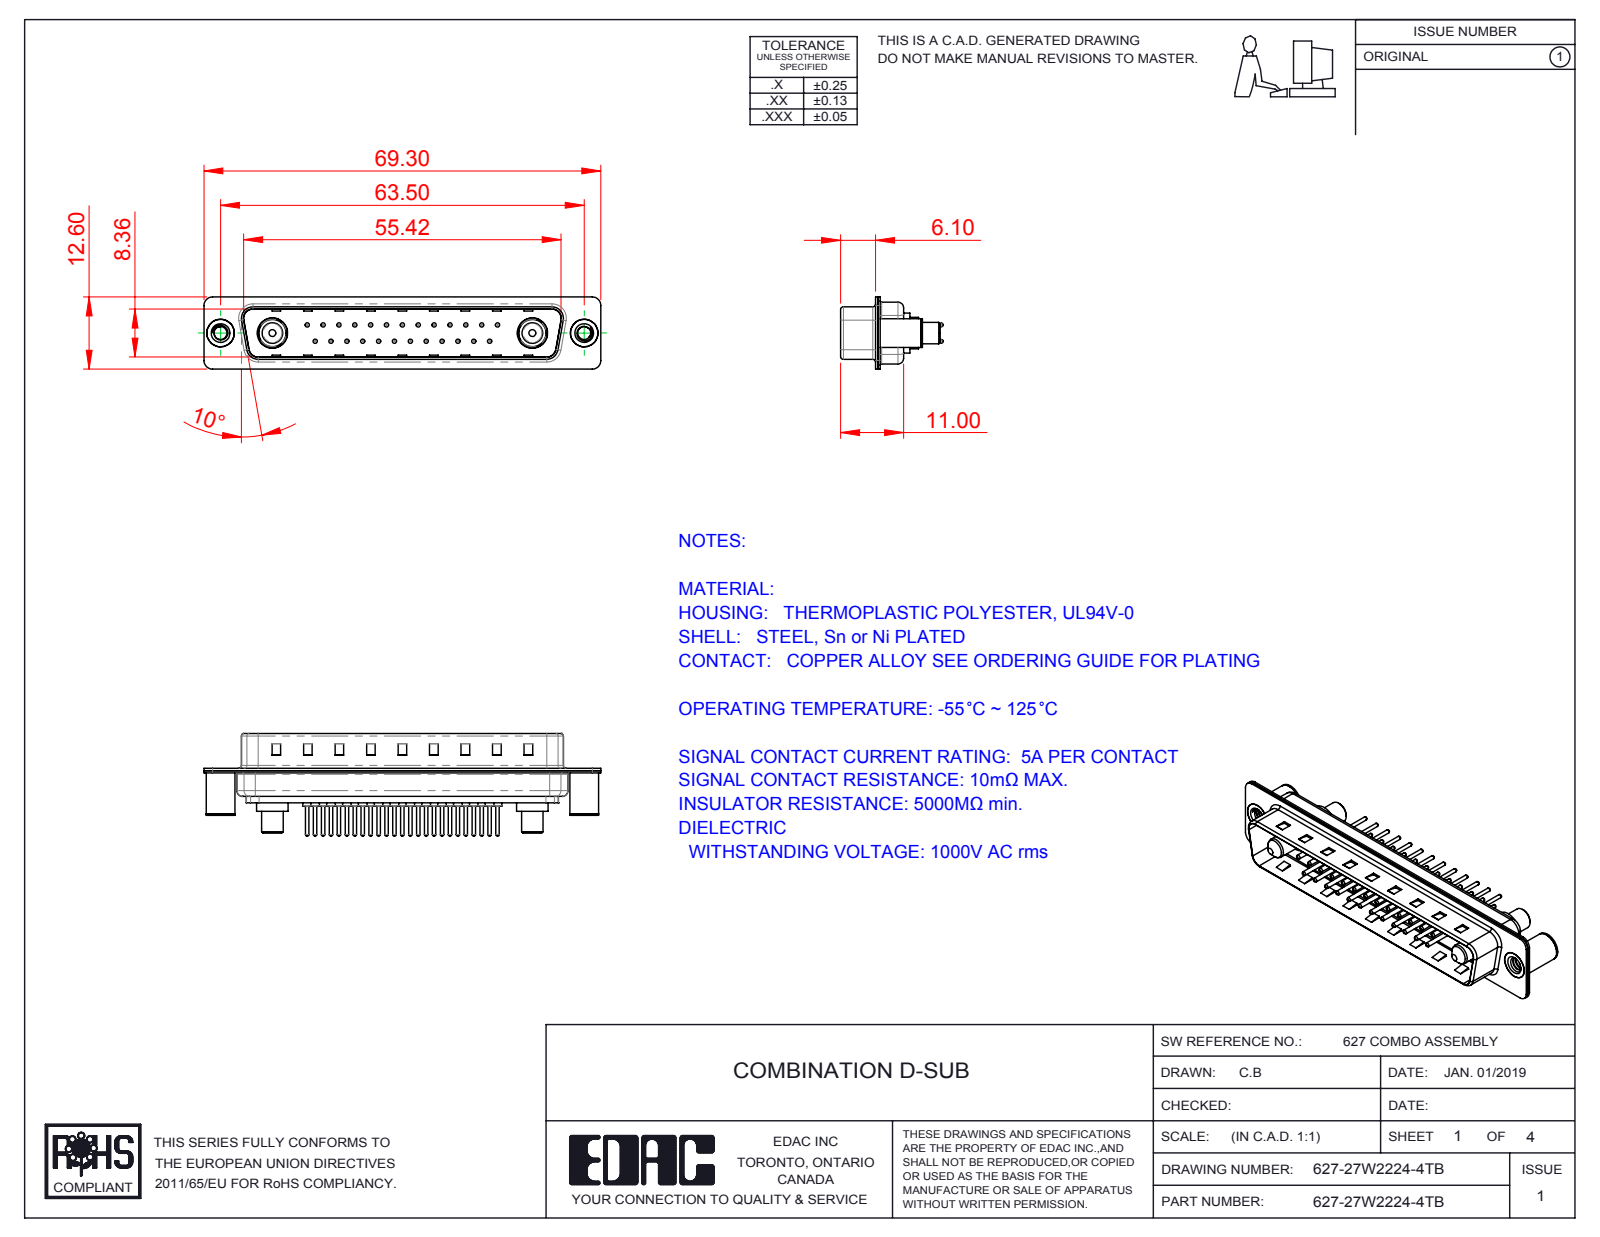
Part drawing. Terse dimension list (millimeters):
name: 627Combo Contact Row 1_24; 627-27W2224-4TB; 627Combo Housing_27W2; 627Combo Shell Rear_37 Contacts (+5 more)
written by: SolidWorks 2016 (CONFIG_CONTROL_DESIGN)
unit: mm
bodies: 34 solids, 1455 faces (398 planar, 557 cylindrical, 500 other)
size: 69.3 × 17.9 × 12.6
volume: 4 058 mm³; area: 9 335 mm²
holes: 25× ⌀0.75, 25× ⌀1.6, 25× ⌀2, 2× ⌀2.26, 2× ⌀3.26, 2× ⌀4, 2× ⌀4.8, 2× ⌀4.85, 2× ⌀5.3
bosses: 25× ⌀1.5, 25× ⌀0.6, 2× ⌀5.5, 2× ⌀5.2, 2× ⌀5, 2× ⌀4.9, 2× ⌀4.75, 2× ⌀3.75
rounds: 16× R1.5, 12× R2, 8× R0.5, 8× R1.6, 4× R0.25, 4× R0.6, 4× R0.65, 4× R0.9
face distances: 0.4, 0.82, 9.58, 8.76, 1.5, 5.6, 1.22, 9.98, 0.42, 9.18
hole spacings: 3.16, 2.77, 5.54, 8.31, 5.03, 7.48, 11.08, 5.04
